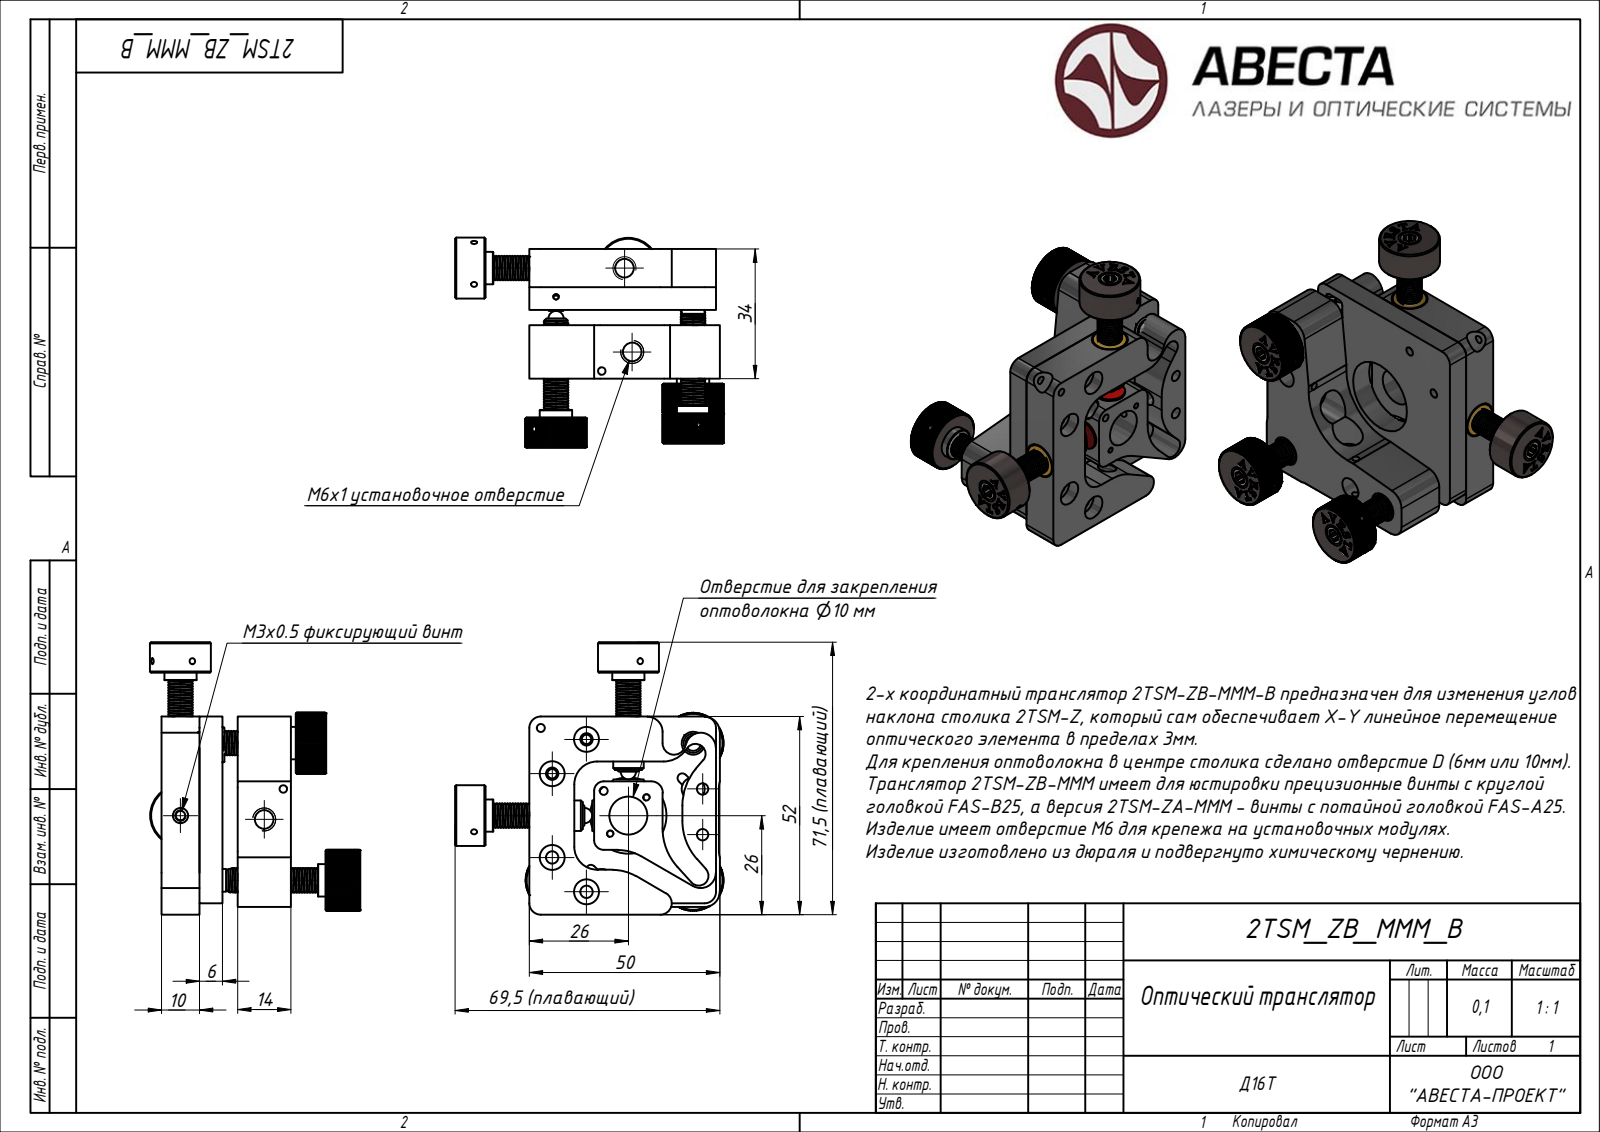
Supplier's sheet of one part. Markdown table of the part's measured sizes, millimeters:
| quantity | value |
| --- | --- |
| part name | Block 02; Block 01 |
| STEP written by | ST-DEVELOPER v15 (AUTOMOTIVE_DESIGN) |
| units | millimeters |
| bodies | 7 solids, 1409 faces (0 planar, 0 cylindrical, 1409 other) |
| overall size | 71.5 × 70.5 × 55.2 |
